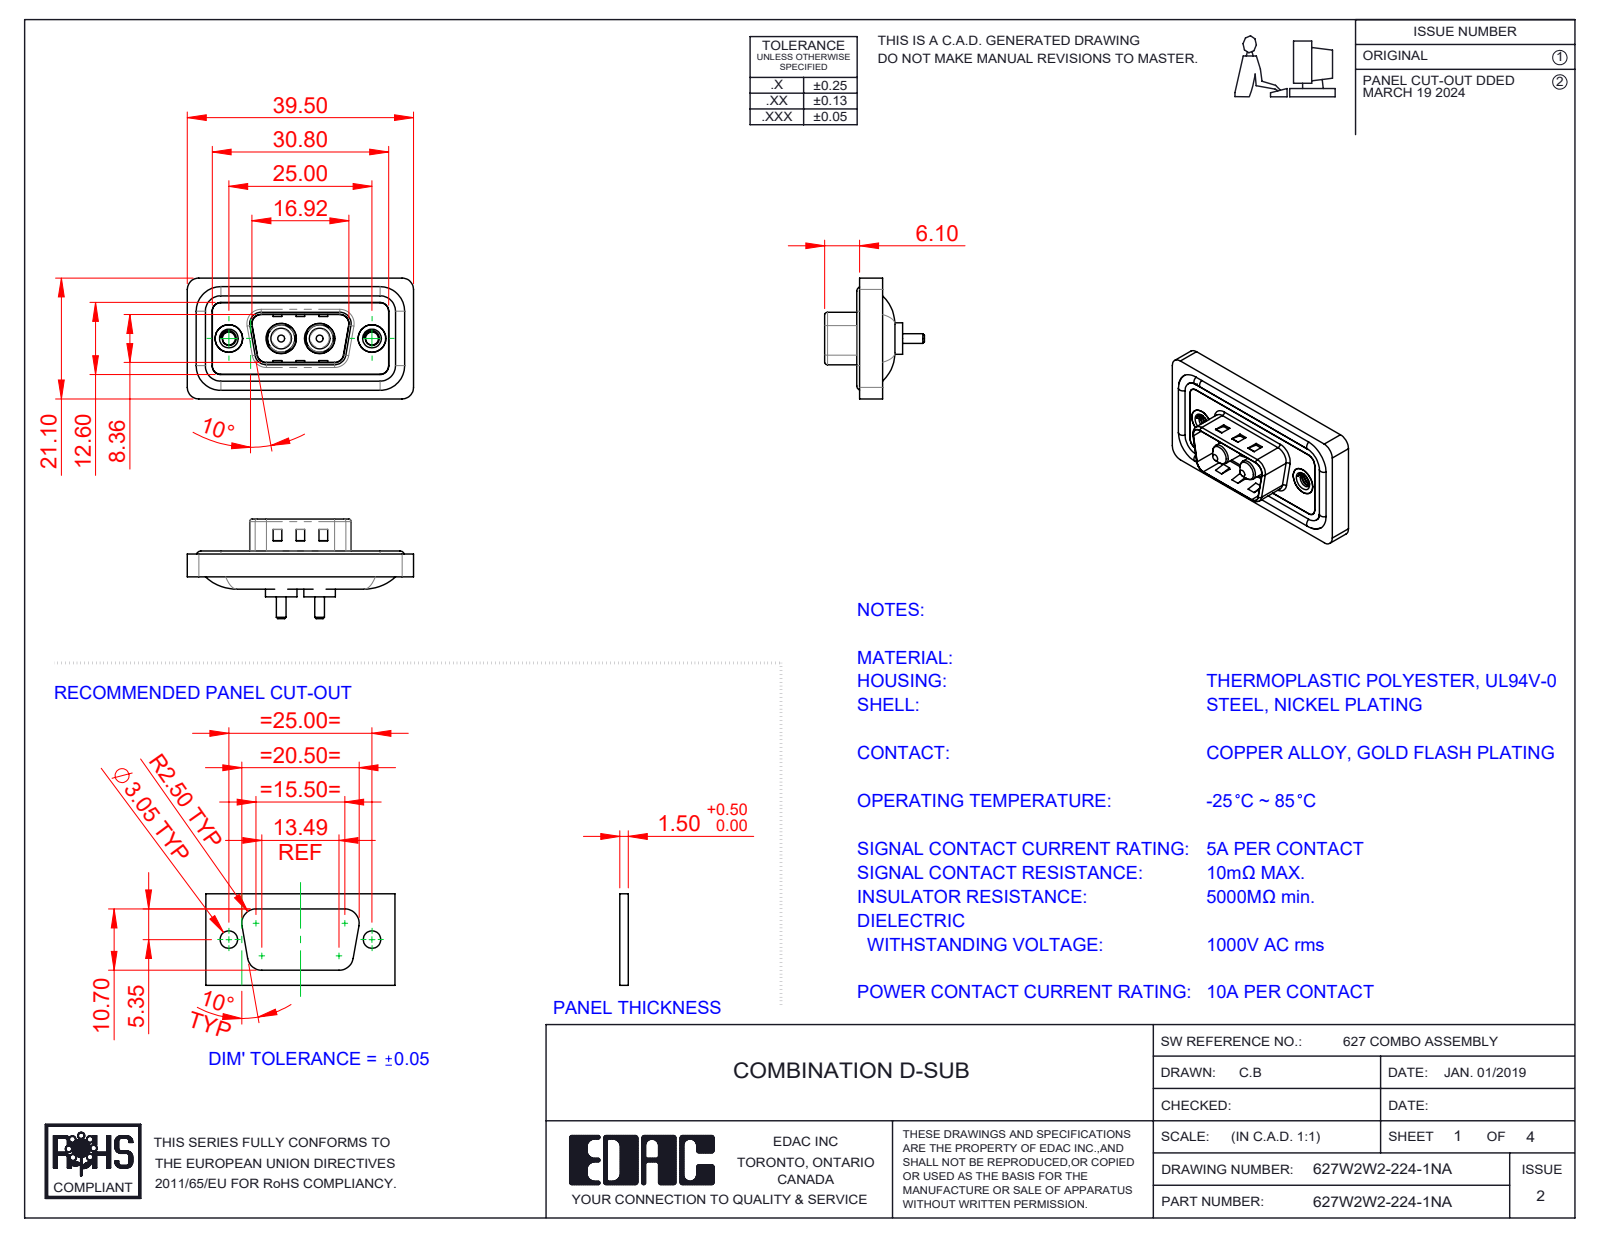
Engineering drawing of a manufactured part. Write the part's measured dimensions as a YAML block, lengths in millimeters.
part_name: "627W2W2-224-1NA; 627Combo Threaded Rivet_A; 627Combo Waterproof Housing_09 Contacts; 627Combo Housing_2W2 (+3 more)"
step_written_by: "SolidWorks 2023 (CONFIG_CONTROL_DESIGN)"
units: millimeters
bodies: {solids: 11, faces: 487, planar: 165, cylindrical: 220, other: 102}
overall_size: [39.5, 21.1, 17.4]
volume: 4433
surface_area: 6956
round_holes:
  - {diameter: 2.26, count: 2}
  - {diameter: 4, count: 2}
  - {diameter: 4.8, count: 2}
  - {diameter: 4.85, count: 2}
  - {diameter: 5, count: 2}
  - {diameter: 5.3, count: 2}
round_bosses_or_shafts:
  - {diameter: 1.6, count: 4}
  - {diameter: 5.5, count: 2}
  - {diameter: 5.2, count: 2}
  - {diameter: 4.9, count: 2}
  - {diameter: 4.75, count: 2}
  - {diameter: 3.75, count: 2}
  - {diameter: 3.6, count: 2}
  - {diameter: 1.7, count: 2}
partial_cylinders:
  - {radius: 1.5, count: 22}
  - {radius: 2, count: 18}
  - {radius: 0.5, count: 8}
  - {radius: 1.6, count: 8}
  - {radius: 0.25, count: 4}
  - {radius: 0.6, count: 4}
  - {radius: 0.65, count: 4}
  - {radius: 0.9, count: 4}
face_to_face_distances: [0.4, 1.1, 2.9, 3.1, 0.5, 1.5, 1.6, 4, 2.5, 0.7]
hole_center_spacings: [9.14, 15.86, 6.72, 25]
